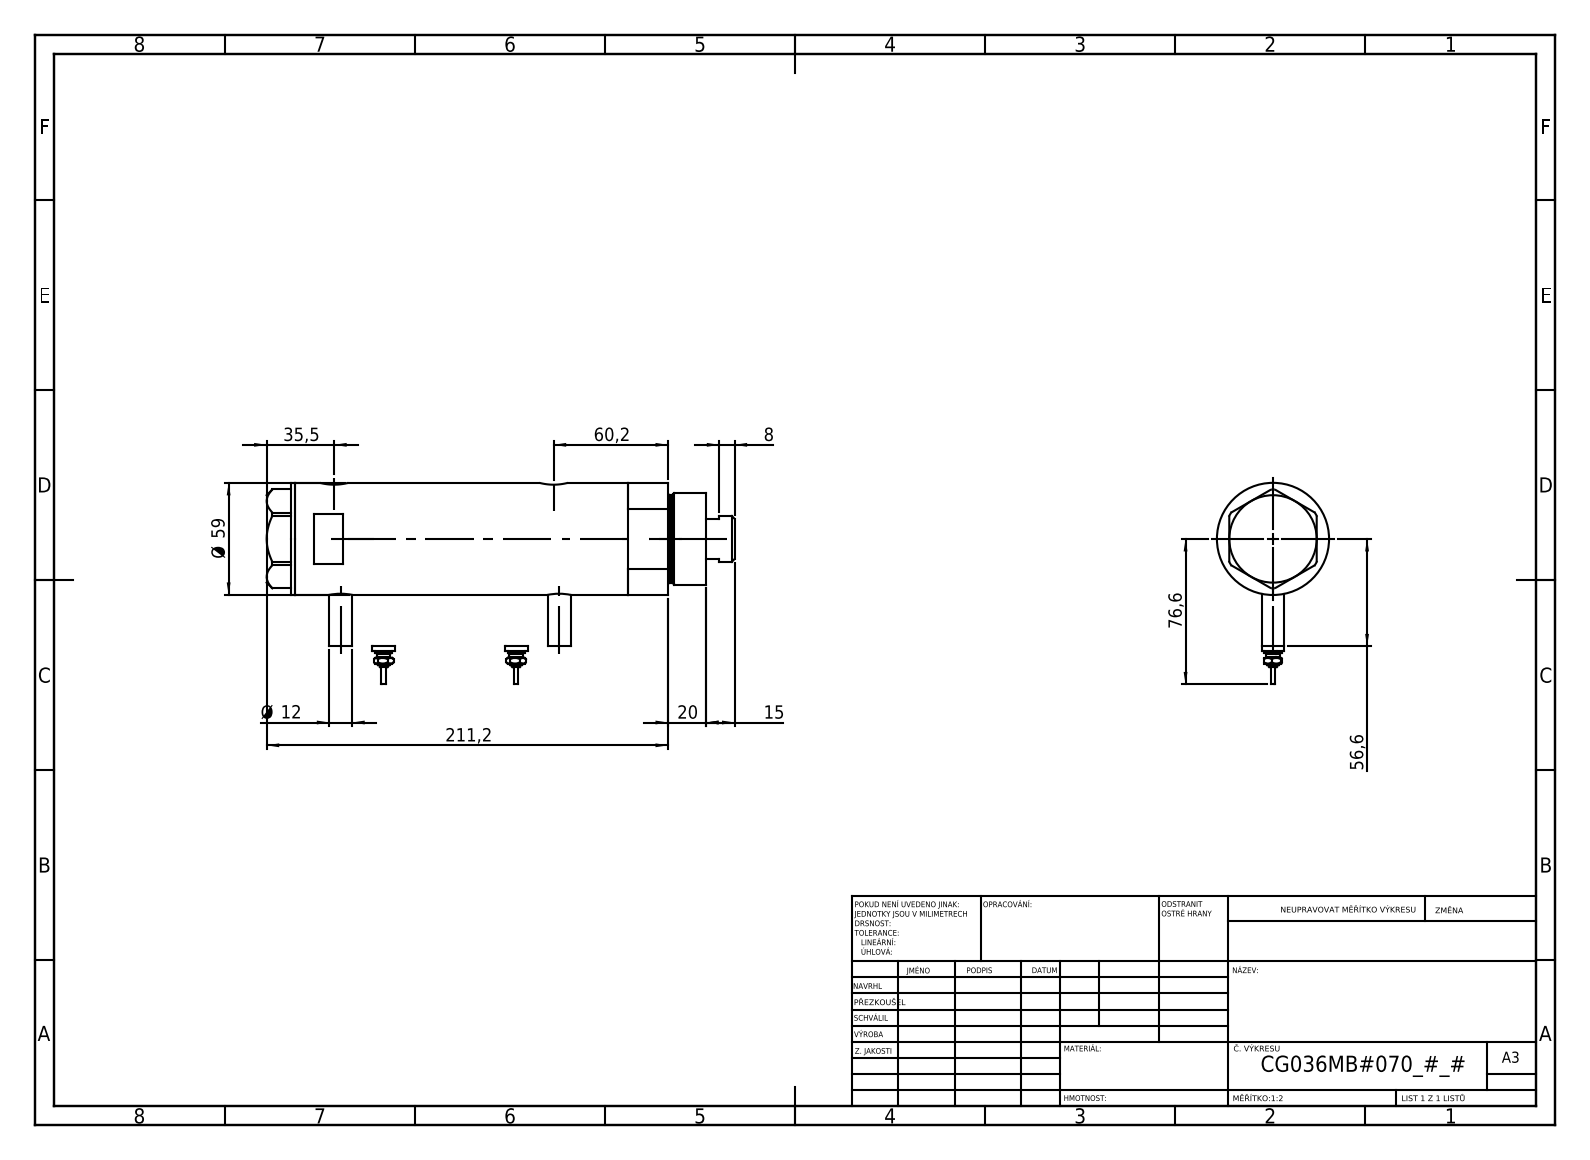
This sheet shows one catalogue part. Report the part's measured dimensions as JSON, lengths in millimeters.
{"part_name": "V270CG_VC; V270CG_BACK; Switch; V270CG_MIDDLE (+1 more)", "step_written_by": "SolidWorks 2019 (CONFIG_CONTROL_DESIGN)", "units": "millimeters", "bodies": {"solids": 6, "faces": 212, "planar": 79, "cylindrical": 69, "other": 64}, "overall_size": [246.2, 106.1, 59], "volume_mm3": 569607, "surface_area_mm2": 116466, "round_holes": [[9.73, 2], [12.5, 2], [15, 2], [8.5, 1], [25, 1], [26.5, 1], [36, 1], [40, 1], [52, 1]], "round_bosses_or_shafts": [[12, 4], [9, 2], [7, 2], [4.5, 2], [2.5, 2], [59, 1], [48, 1], [46, 1]], "face_to_face_distances": [137.2, 23.5, 113.7, 15, 38.5, 152.2, 2, 231.2, 216.2, 192.7], "hole_center_spacings": [2.9, 3.5, 112, 114.9, 115.5, 118.4]}
